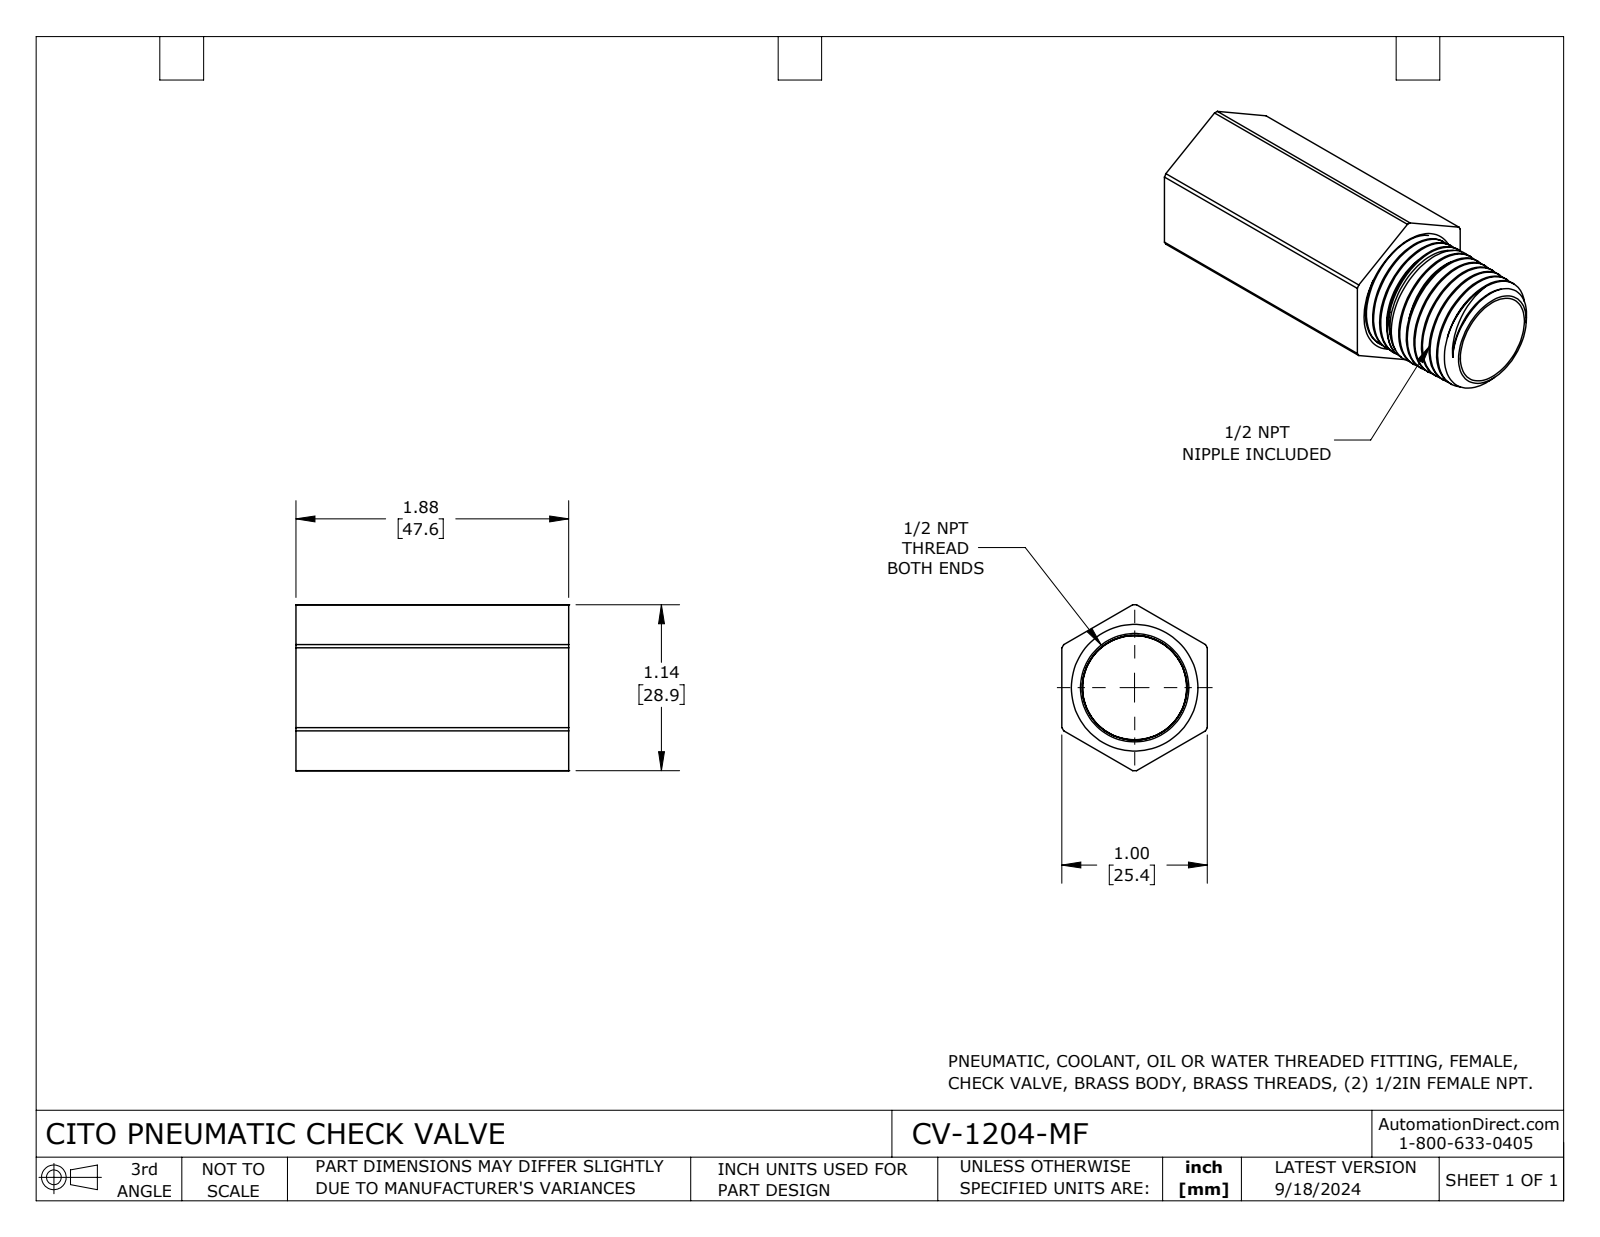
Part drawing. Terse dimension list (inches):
name: CV-1204-MF
written by: SolidWorks 2023 (CONFIG_CONTROL_DESIGN)
unit: in
bodies: 6 solids, 194 faces (40 planar, 64 cylindrical, 90 other)
size: 2.688 × 1.14 × 1
volume: 1.072 in³; area: 21.34 in²
holes: 1× ⌀0.046, 1× ⌀0.086, 1× ⌀0.087, 1× ⌀0.171, 1× ⌀0.622, 1× ⌀0.625, 1× ⌀0.63, 1× ⌀0.691, 1× ⌀0.9
bosses: 1× ⌀0.715, 1× ⌀0.551, 1× ⌀0.26, 1× ⌀0.25, 1× ⌀0.168, 1× ⌀0.085
rounds: 6× R0.005, 6× R0.012, 6× R0.168, 1× R0.306, 1× R0.57
face distances: 1, 1.058, 1.875, 0.817, 1.024, 0.034, 0.85, 0.939, 0.085, 0.119
